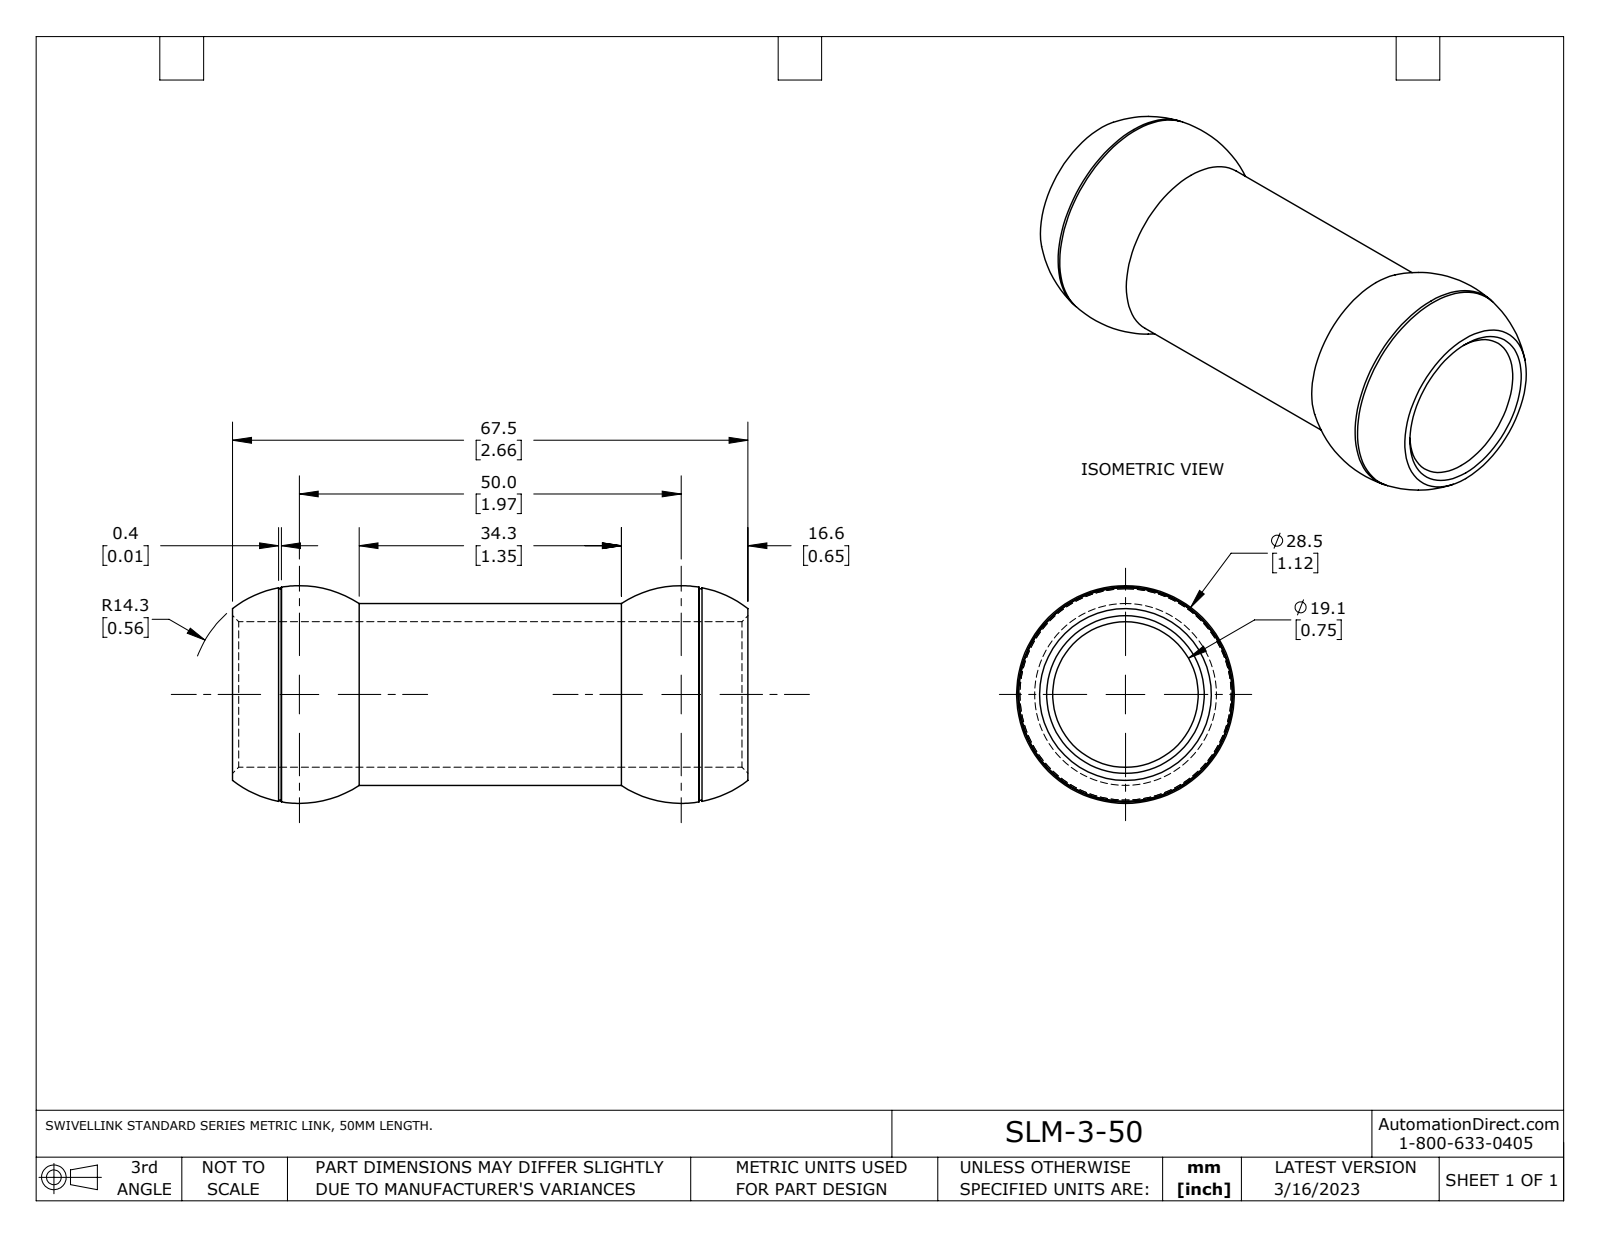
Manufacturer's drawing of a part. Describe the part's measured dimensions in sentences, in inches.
The part is named "SLM-3-50". Its 3-D file was written by "SolidWorks 2021 (AUTOMOTIVE_DESIGN)". It is 2 solids with 14 faces: 2 planar, 2 cylindrical and 10 other. Overall it measures 3.091 by 1.107 by 1.107 inches. Its volume is 2.063 cubic inches and its surface area 17.42 square inches. Round bosses or shafts: 1 of diameter 0.937, 1 of diameter 0.75. The main face-to-face distances are 2.657.
